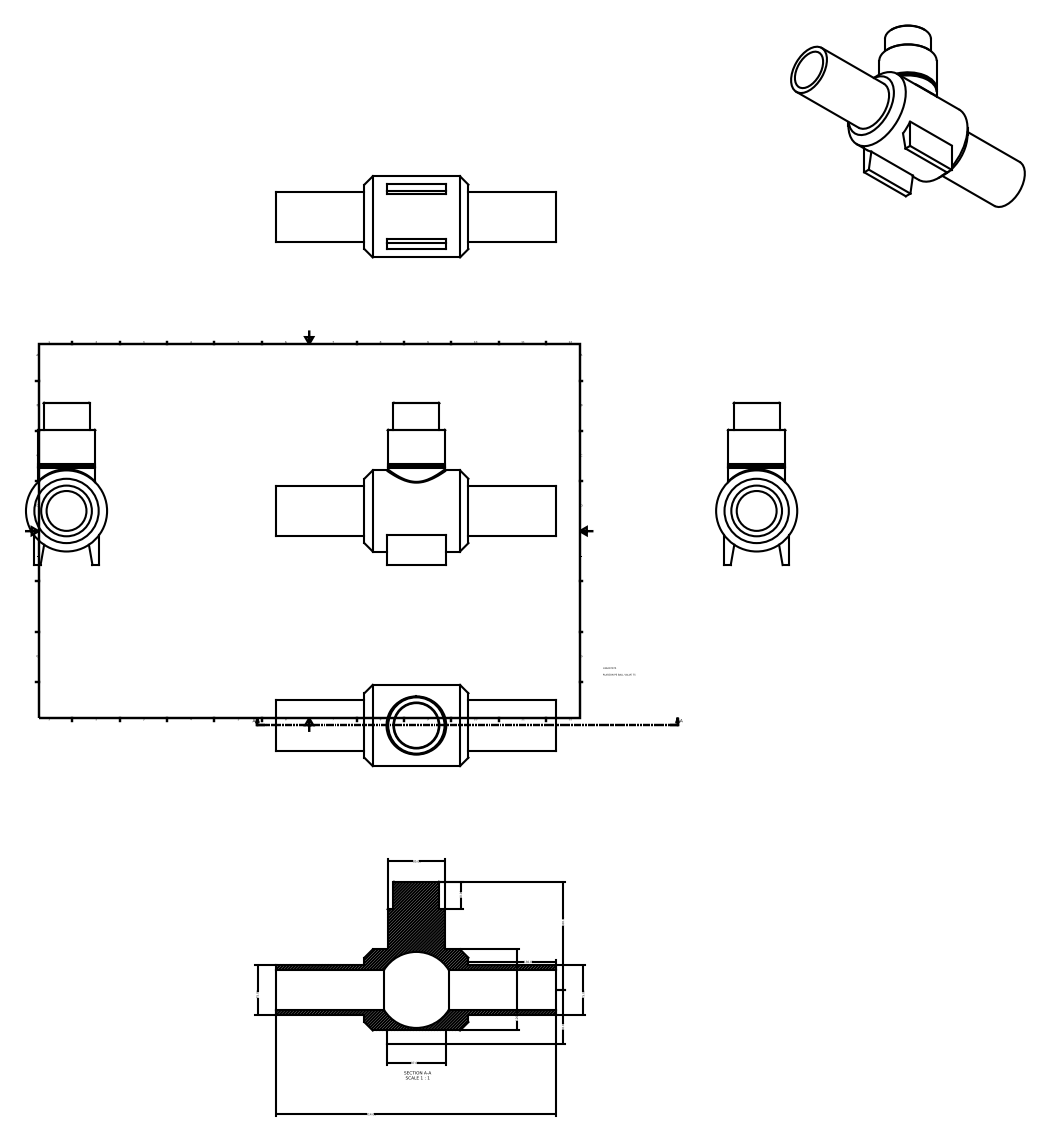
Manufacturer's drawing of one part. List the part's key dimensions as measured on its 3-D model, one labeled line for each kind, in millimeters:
Part name (STEP PRODUCT): 436207075
STEP written by: Autodesk Inventor 2015 (AUTOMOTIVE_DESIGN)
Units: millimetres
Bodies: 1 solid, 33 faces (16 planar, 9 cylindrical, 8 other)
Overall size (bounding box): 414 × 240 × 120
Volume: 1 832 000 mm³ · Surface area: 262 838 mm²
Round holes (diameter × count): ⌀59 ×1
Round bosses / shafts (diameter × count): ⌀120 ×1, ⌀85 ×1, ⌀75 ×1, ⌀68 ×1
Main face-to-face distances: 96, 130, 284, 154, 163.5, 250.5, 33.5, 120.5, 40, 414
